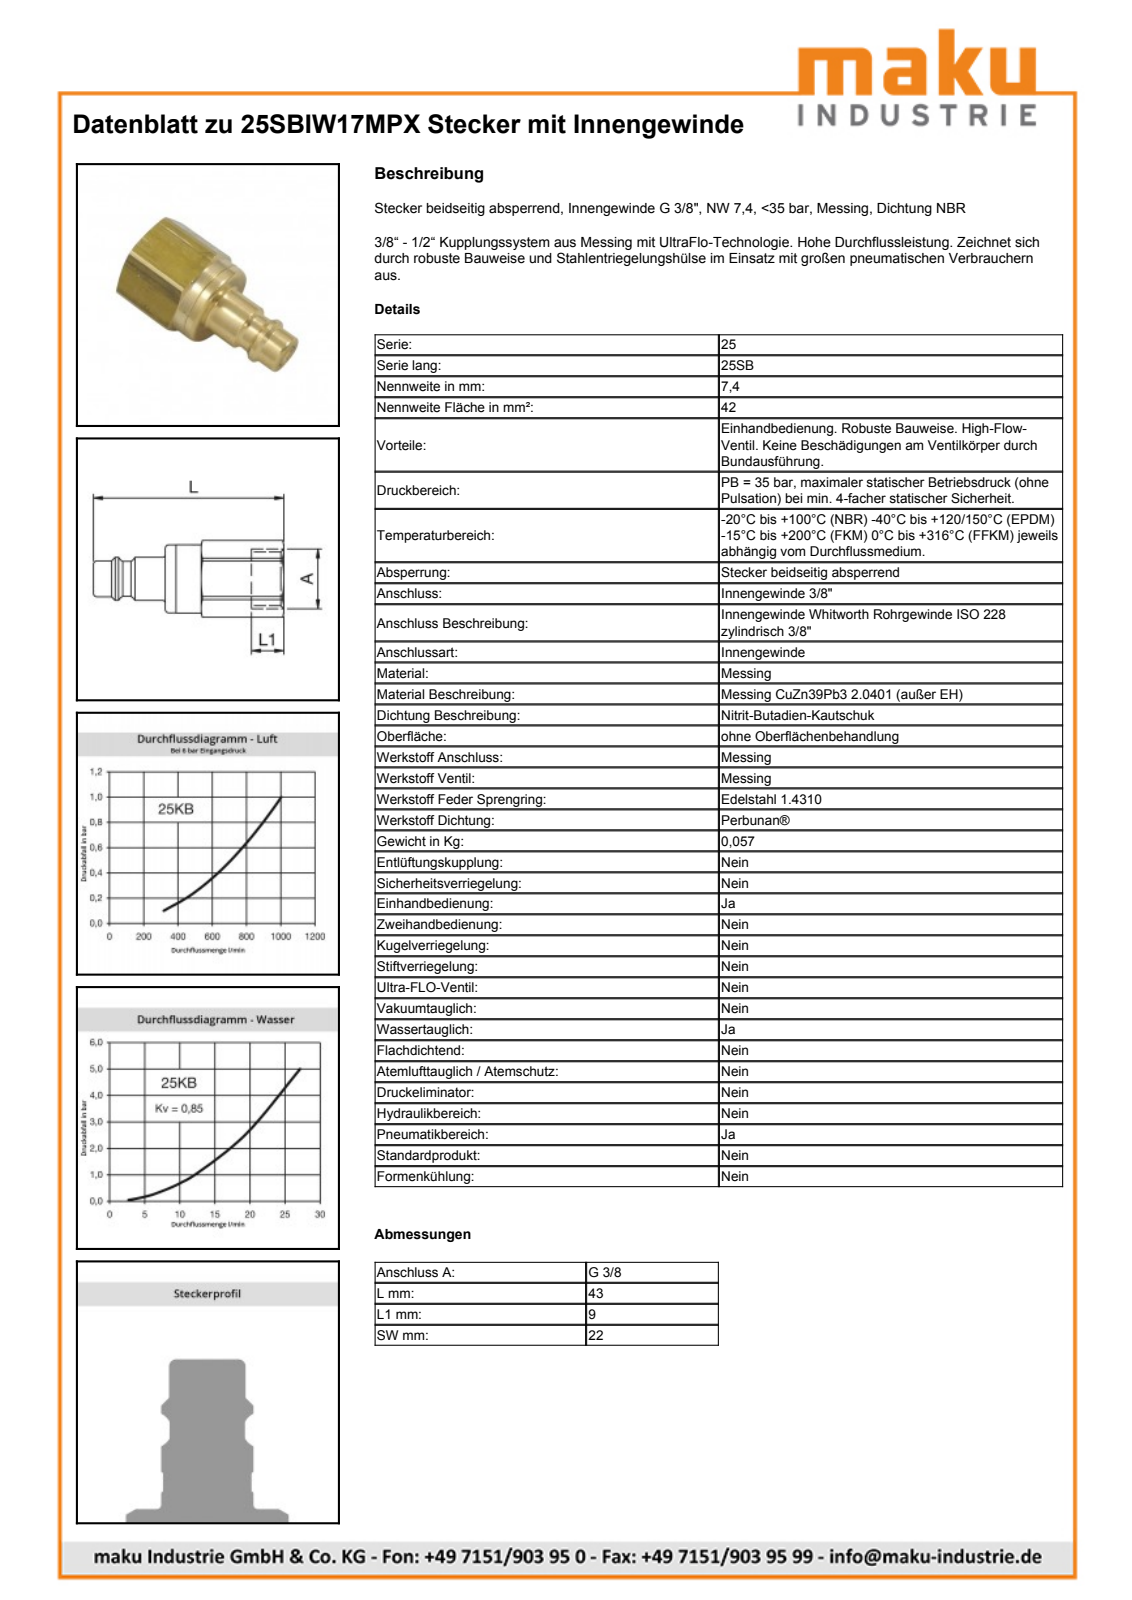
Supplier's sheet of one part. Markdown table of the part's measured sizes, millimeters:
| quantity | value |
| --- | --- |
| part name | D113335 |
| STEP written by | Autodesk Inventor 2013 (AUTOMOTIVE_DESIGN) |
| units | millimeters |
| bodies | 1 solid, 54 faces (15 planar, 15 cylindrical, 24 other) |
| overall size | 43.1 × 24.68 × 23.4 |
| volume | 9 395 mm³ |
| surface area | 4 126 mm² |
| round holes (diameter × count) | 14.95 × 1, 17 × 1 |
| round bosses / shafts (diameter × count) | 21 × 1, 16.5 × 1, 12 × 1, 10 × 1, 9.75 × 1 |
| partial cylindrical surfaces (radius × count) | 12.4 × 1 |
| main face-to-face distances | 22, 9, 14.1, 23.1, 3, 4.5, 20, 34.1, 43.1, 23 |
